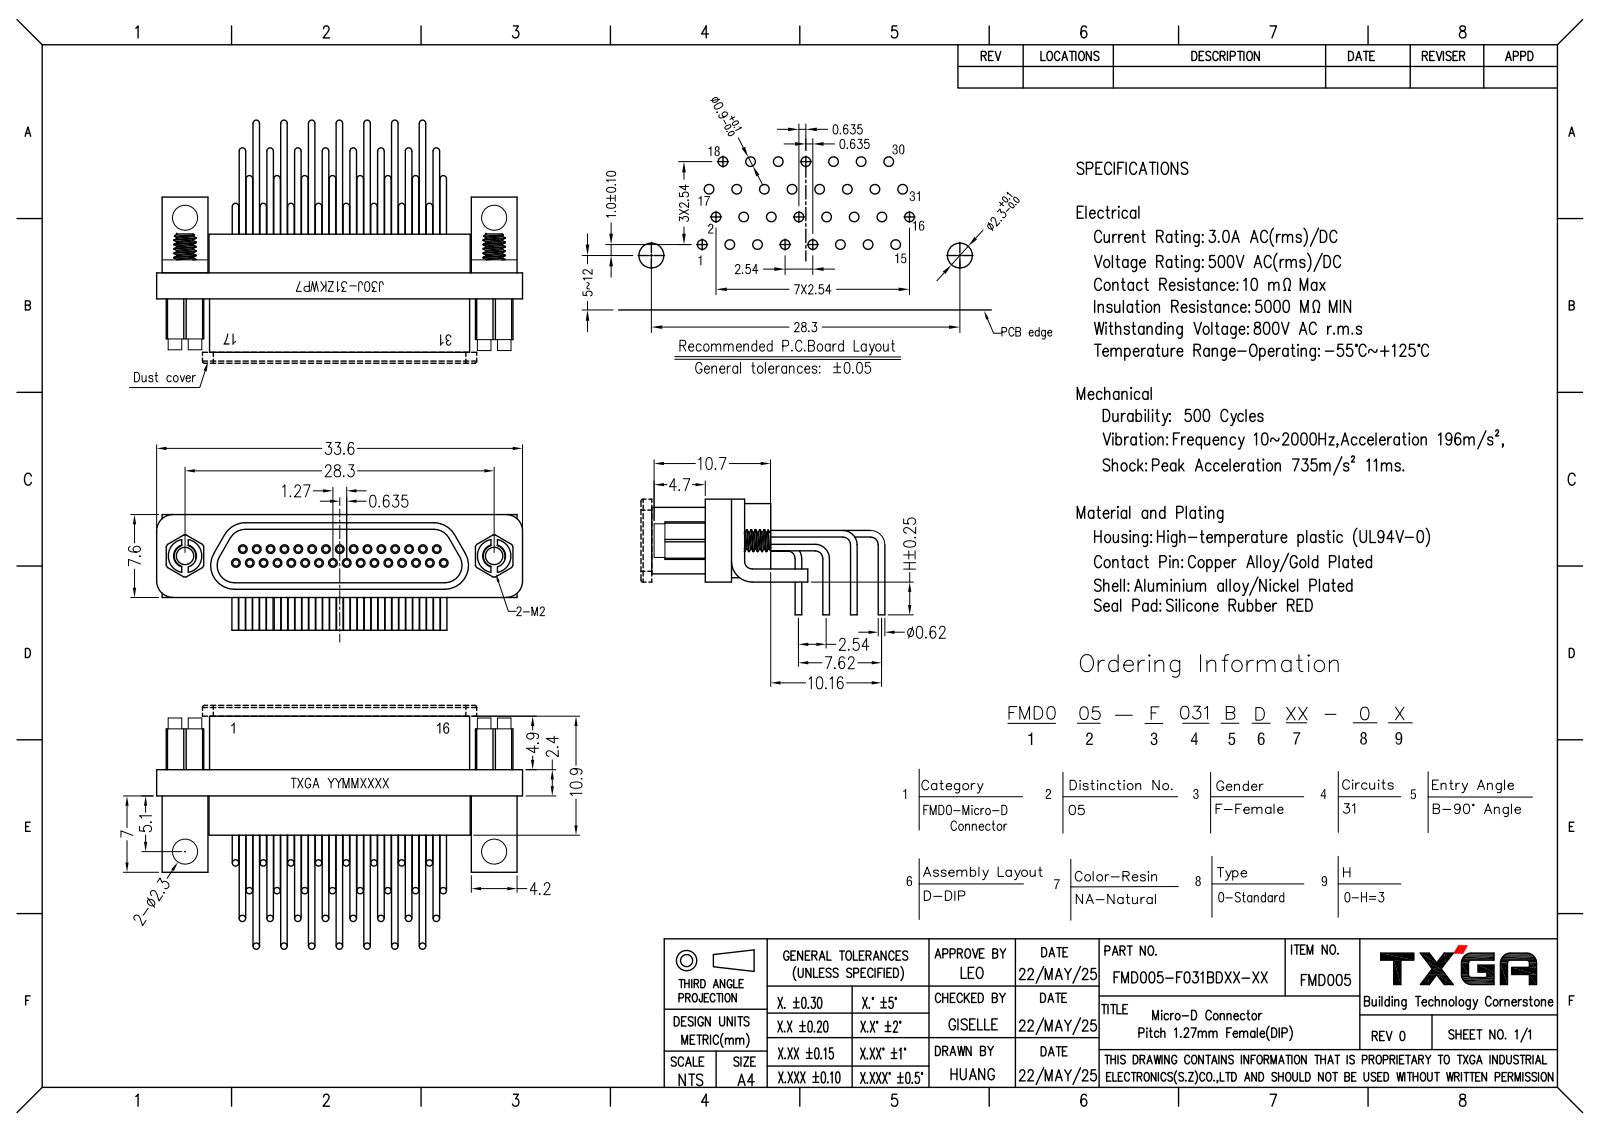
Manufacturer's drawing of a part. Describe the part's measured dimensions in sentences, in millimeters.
The part is named "FMD005-F031BDRD-00". Its 3-D file was written by "SolidWorks 2021 (CONFIG_CONTROL_DESIGN)". It is 1 solid with 1496 faces: 658 planar, 394 cylindrical and 444 other. Overall it measures 33.6 by 21.36 by 10.6 millimeters. Its volume is 1 570 cubic millimeters and its surface area 3 009 square millimeters. Round holes: 31 of diameter 0.6, 2 of diameter 1.6, 2 of diameter 1.8, 2 of diameter 2.3. Round bosses or shafts: 31 of diameter 0.8, 31 of diameter 0.6, 2 of diameter 3.1, 2 of diameter 2. Partial cylindrical surfaces (rounded edges, fillets, slot ends): 12 of radius 0.3, 4 of radius 1.5, 4 of radius 1.6, 4 of radius 1.8, 4 of radius 2.2, 2 of radius 1.15, 1 of radius 0.7, 1 of radius 1.9. The main face-to-face distances are 0.6, 6, 5.5, 0.75, 1.35, 6.25, 6.85, 0.35, 0.95, 0.4. The hole center spacings are 1.27, 2.2, 2.54, 3.36, 3.81, 5.08, 6.35, 7.62.
